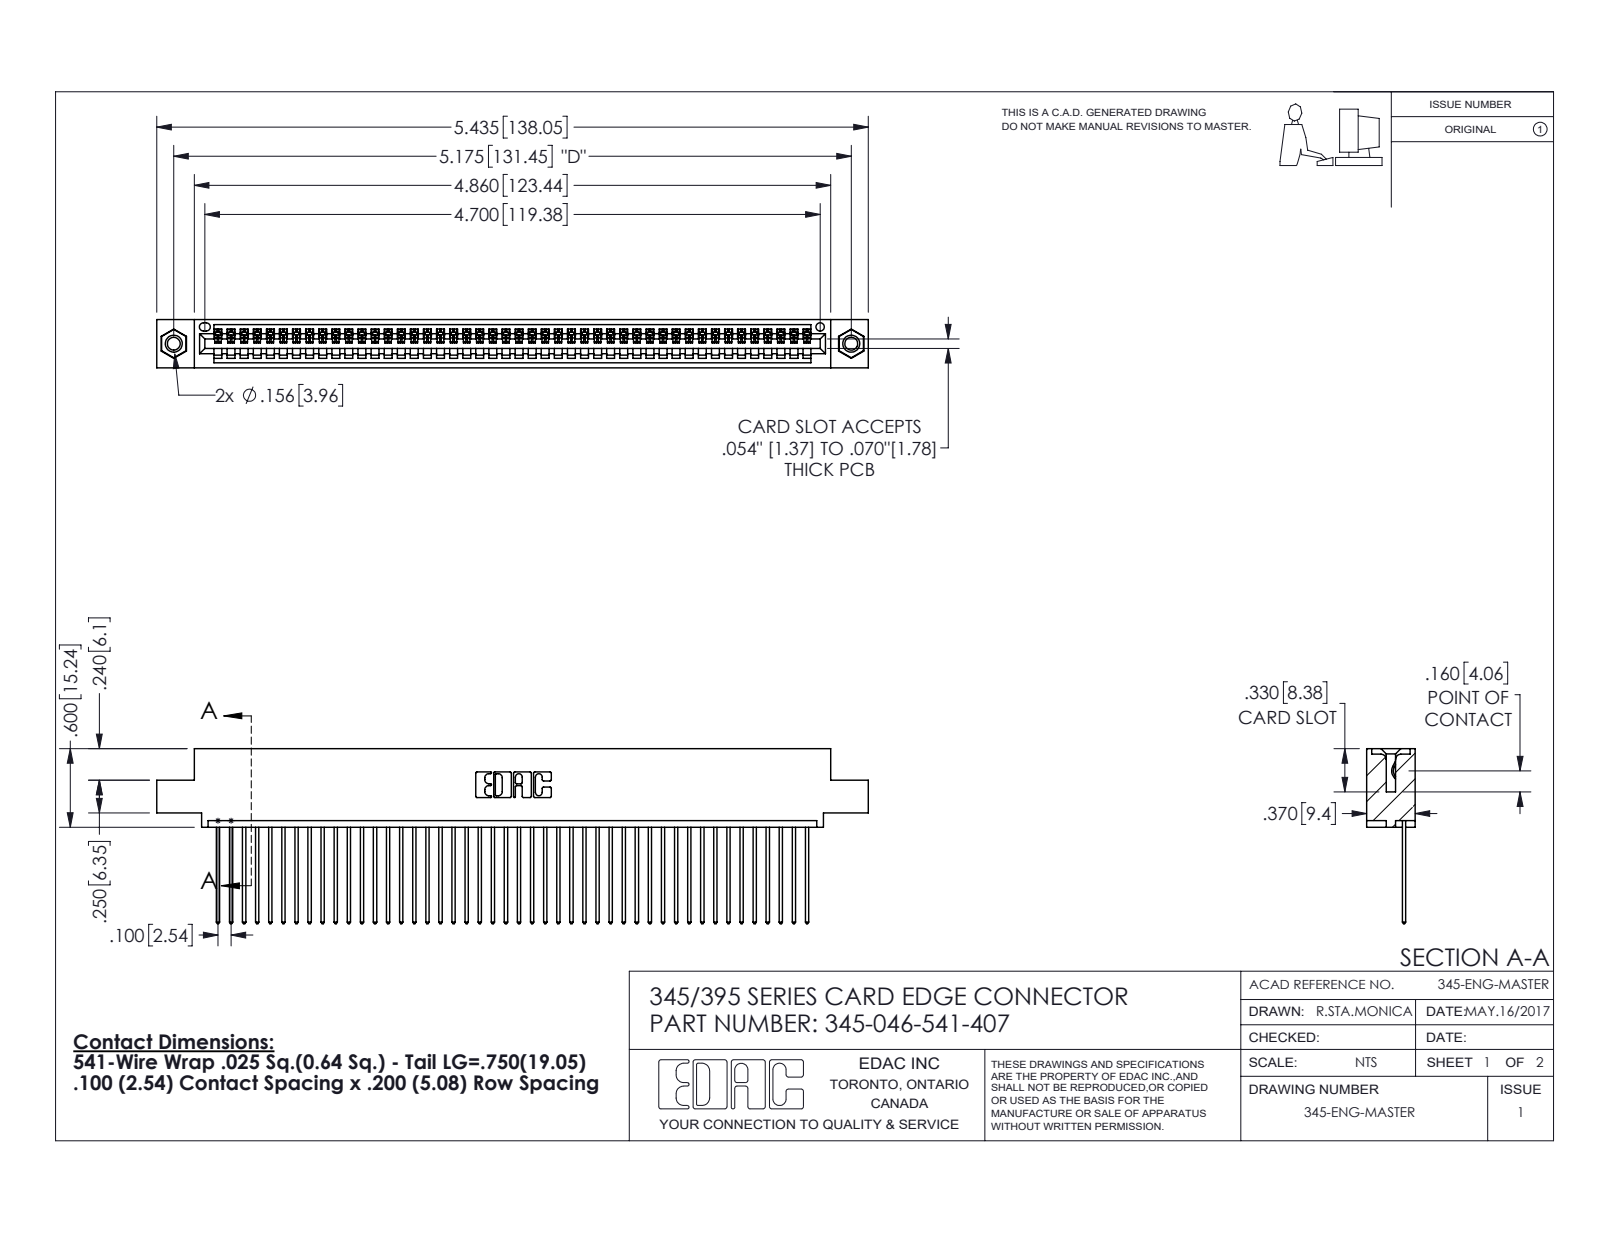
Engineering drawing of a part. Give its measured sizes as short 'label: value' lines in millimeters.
name: 345 Part_0.110 Offset - 0.156 Dia-TI; 345-250-001_345-250-005-103; 345-046-541-407; 345-292-001_345-293-141
written by: SolidWorks 2016 (CONFIG_CONTROL_DESIGN)
unit: mm
bodies: 49 solids, 2858 faces (1956 planar, 886 cylindrical, 16 other)
size: 138 × 34 × 9.4
volume: 13 200 mm³; area: 18 620 mm²
holes: 2× ⌀2.5, 2× ⌀3.2, 2× ⌀4, 1× ⌀1.6
bosses: 2× ⌀3.9
rounds: 92× R0.2, 92× R0.3, 22× R0.3, 6× R0.2, 6× R0.8, 3× R0.7, 2× R0.8, 2× R1
face distances: 1.8, 7.6, 2.5, 6.9, 0.6, 9.4, 5.1, 5.7, 3.8, 1.8
hole spacings: 6.9, 125.5, 131.4
